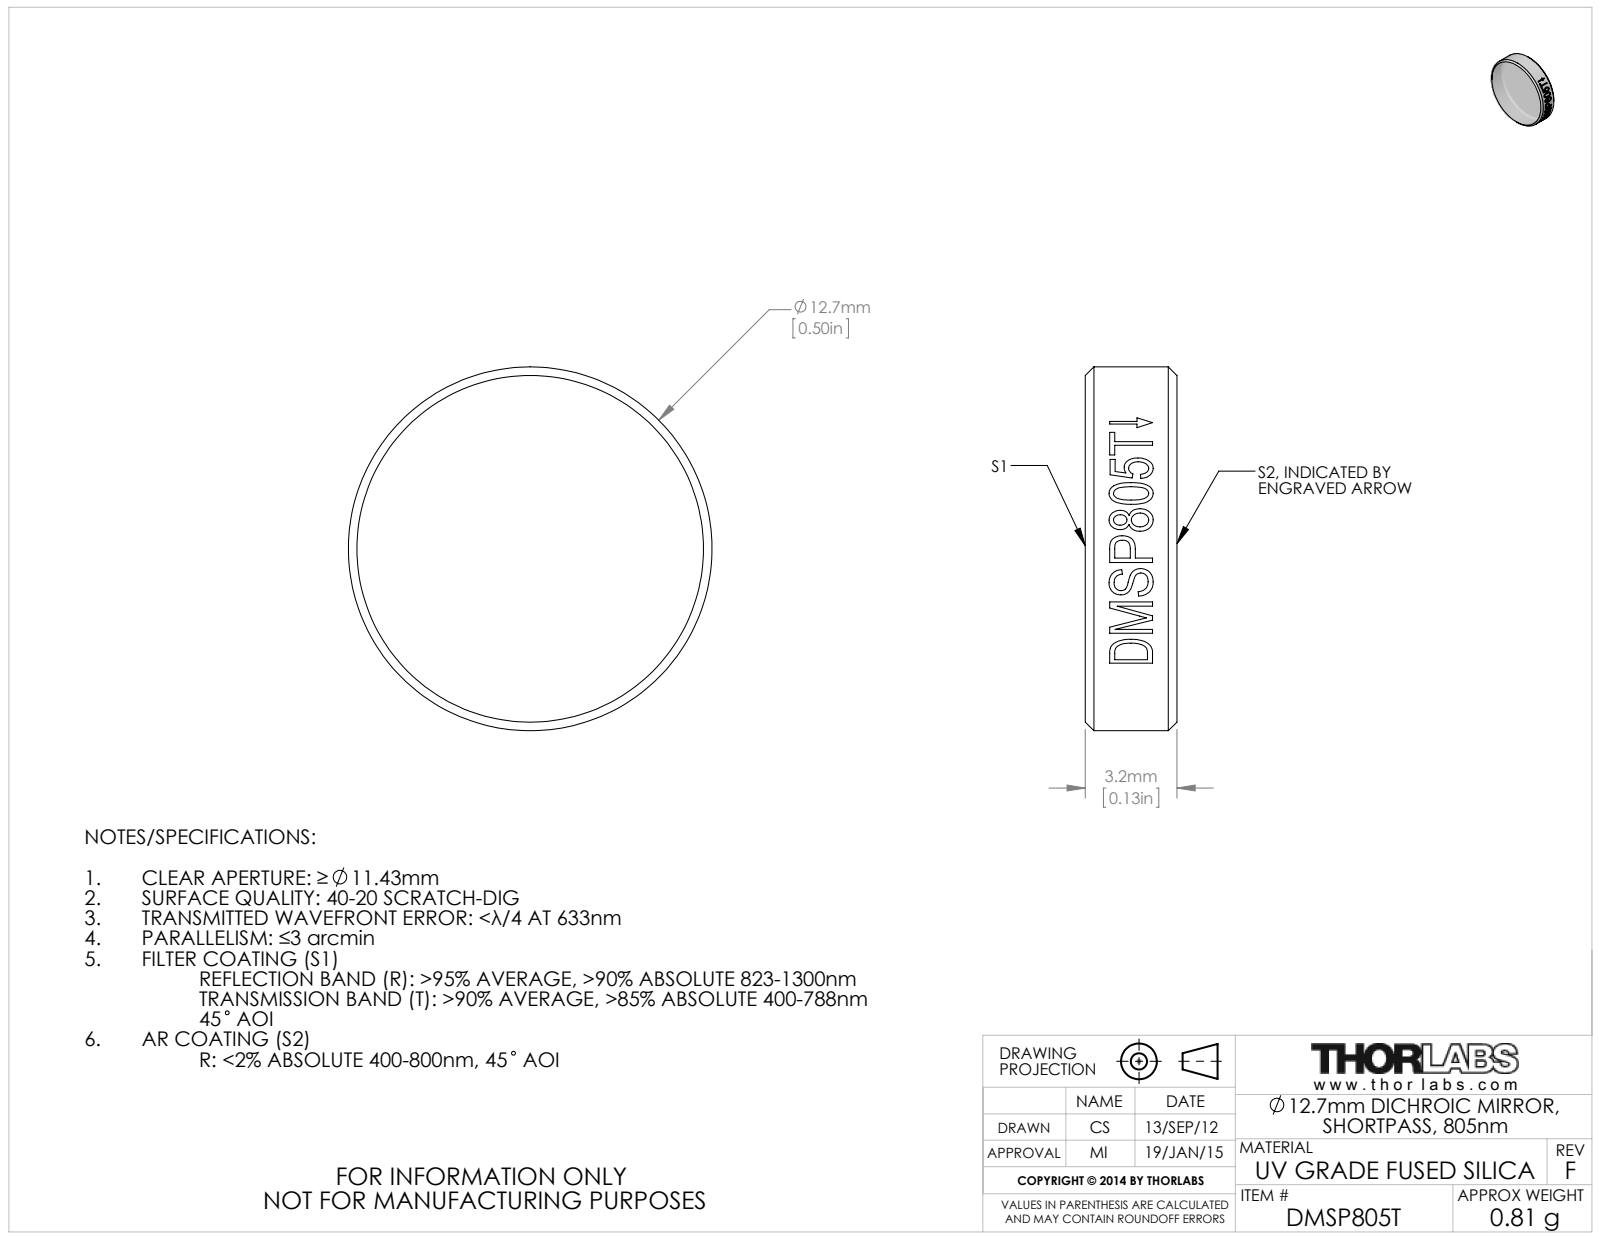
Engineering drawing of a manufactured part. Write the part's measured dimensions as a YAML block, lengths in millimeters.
part_name: "24966-E0W"
step_written_by: "SolidWorks 2011 (CONFIG_CONTROL_DESIGN)"
units: millimeters
bodies: {solids: 0, faces: 22, planar: 2, cylindrical: 16, other: 4}
overall_size: [12.7, 12.7, 3.2]
round_bosses_or_shafts:
  - {diameter: 12.7, count: 1}
face_to_face_distances: [3.2]
